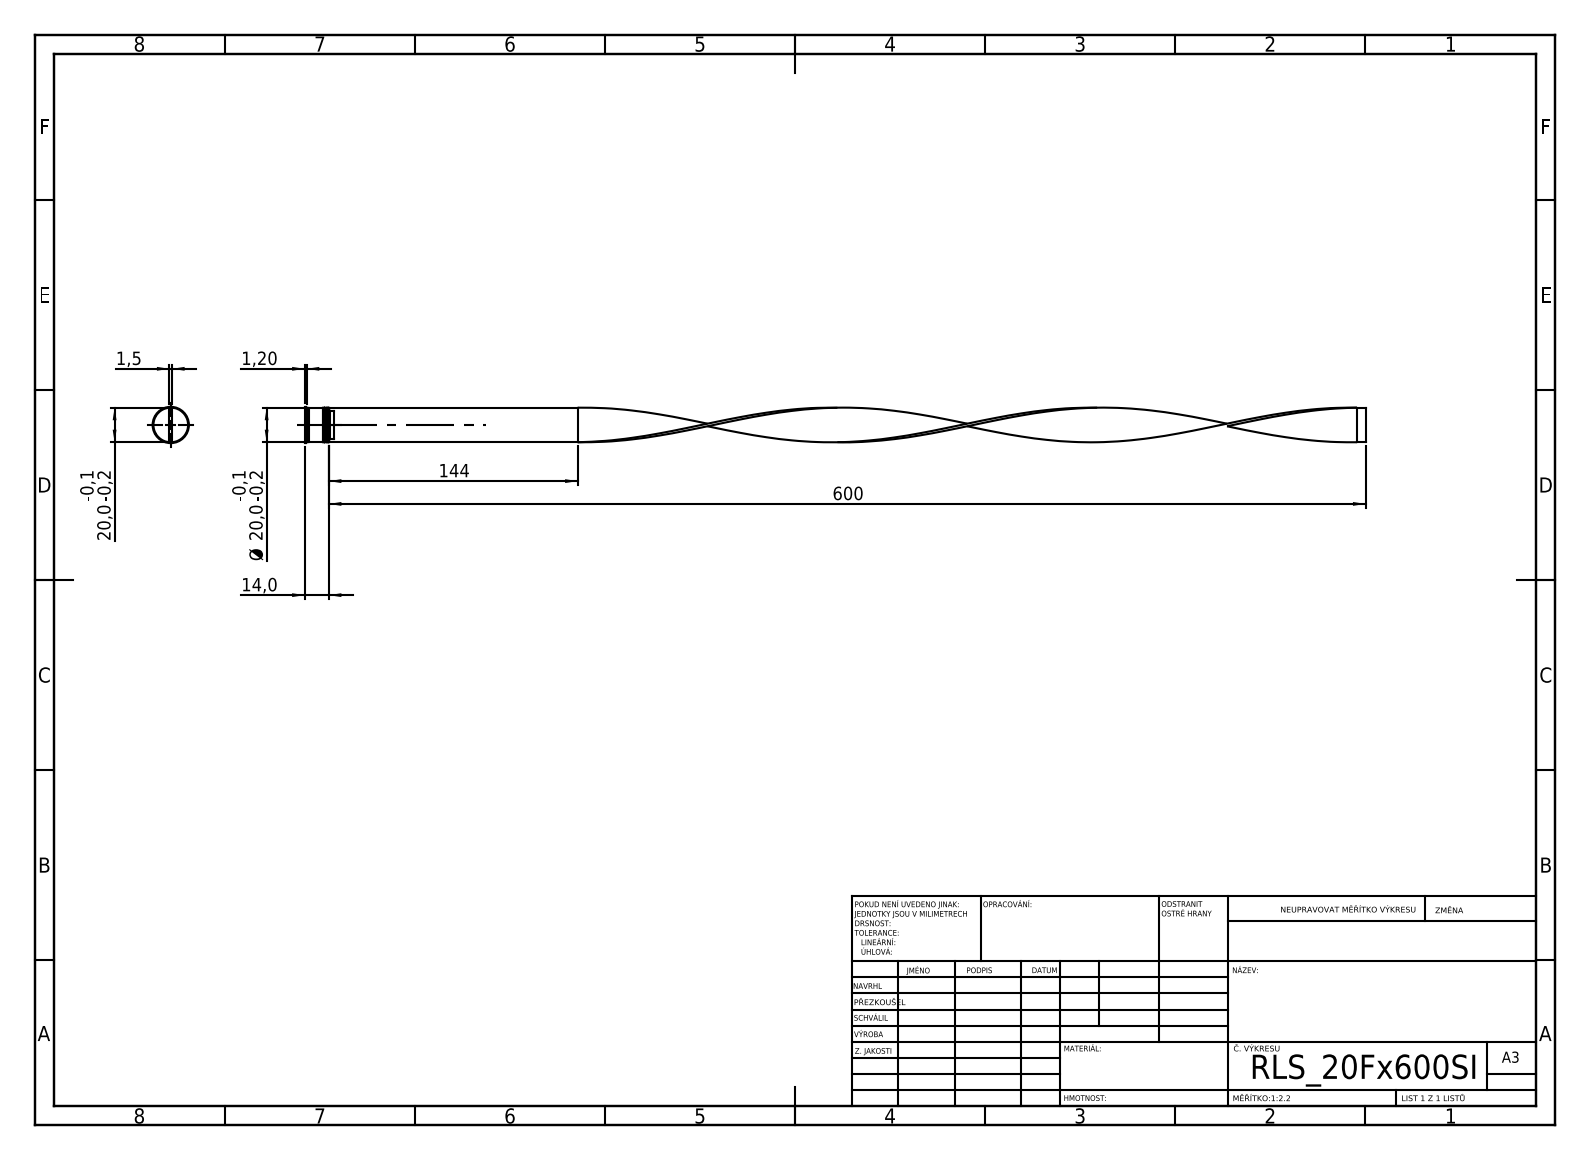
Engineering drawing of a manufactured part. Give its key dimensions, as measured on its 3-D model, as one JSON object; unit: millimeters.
{"step_written_by": "SolidWorks 2019 (CONFIG_CONTROL_DESIGN)", "units": "millimeters", "bodies": {"solids": 3, "faces": 98, "planar": 43, "cylindrical": 28, "other": 27}, "overall_size": [614, 21, 21], "volume_mm3": 23152, "surface_area_mm2": 29035, "round_bosses_or_shafts": [[21, 1], [20, 1], [19.4, 1], [16.8, 1]], "partial_cylinders_radius": [[8.5, 1]], "face_to_face_distances": [1.5, 0.7, 2.2, 0.8, 11.7, 11, 10.2, 9.5, 20, 16]}
